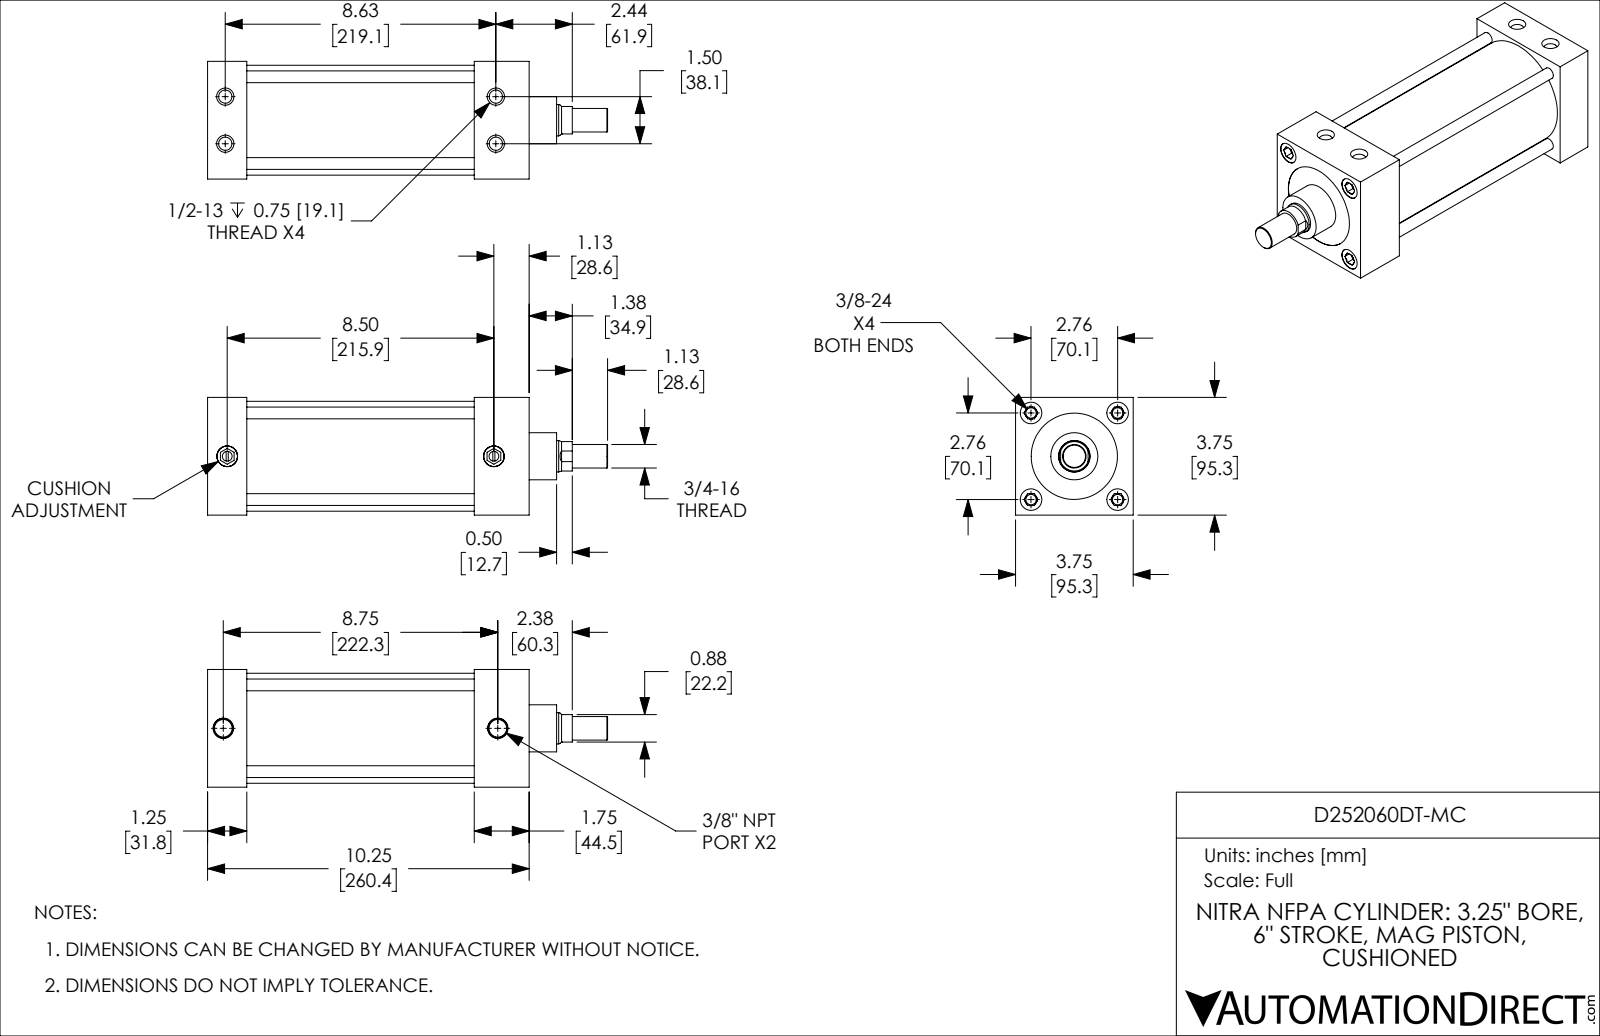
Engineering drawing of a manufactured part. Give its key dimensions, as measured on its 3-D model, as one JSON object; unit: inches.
{"part_name": "D252060DT-MC; D252060DT-MC_CUSHION; D252060DT-MC_BODY; D252060DT-MC_PISTON_KK1", "step_written_by": "SolidWorks 2019 (CONFIG_CONTROL_DESIGN)", "units": "inches", "bodies": {"solids": 4, "faces": 246, "planar": 90, "cylindrical": 78, "other": 78}, "overall_size": [12.75, 3.75, 3.75], "volume_in3": 70.12, "surface_area_in2": 380.1, "round_holes": [[0.332, 4], [0.422, 4], [0.687, 4], [0.312, 2], [0.562, 2], [0.656, 2], [1.001, 1], [2.75, 1], [3.251, 1]], "round_bosses_or_shafts": [[0.375, 4], [0.657, 2], [3.501, 1], [3.249, 1], [1.5, 1], [0.999, 1], [0.75, 1]], "partial_cylinders_radius": [[0.469, 1]], "face_to_face_distances": [1.25, 3.75, 8.5, 7.25, 2.5, 6, 10.25, 9, 7.75, 1.75], "hole_center_spacings": [0.753, 1.952, 2.76, 8.72, 1.5, 3.903, 8.625, 8.754]}
